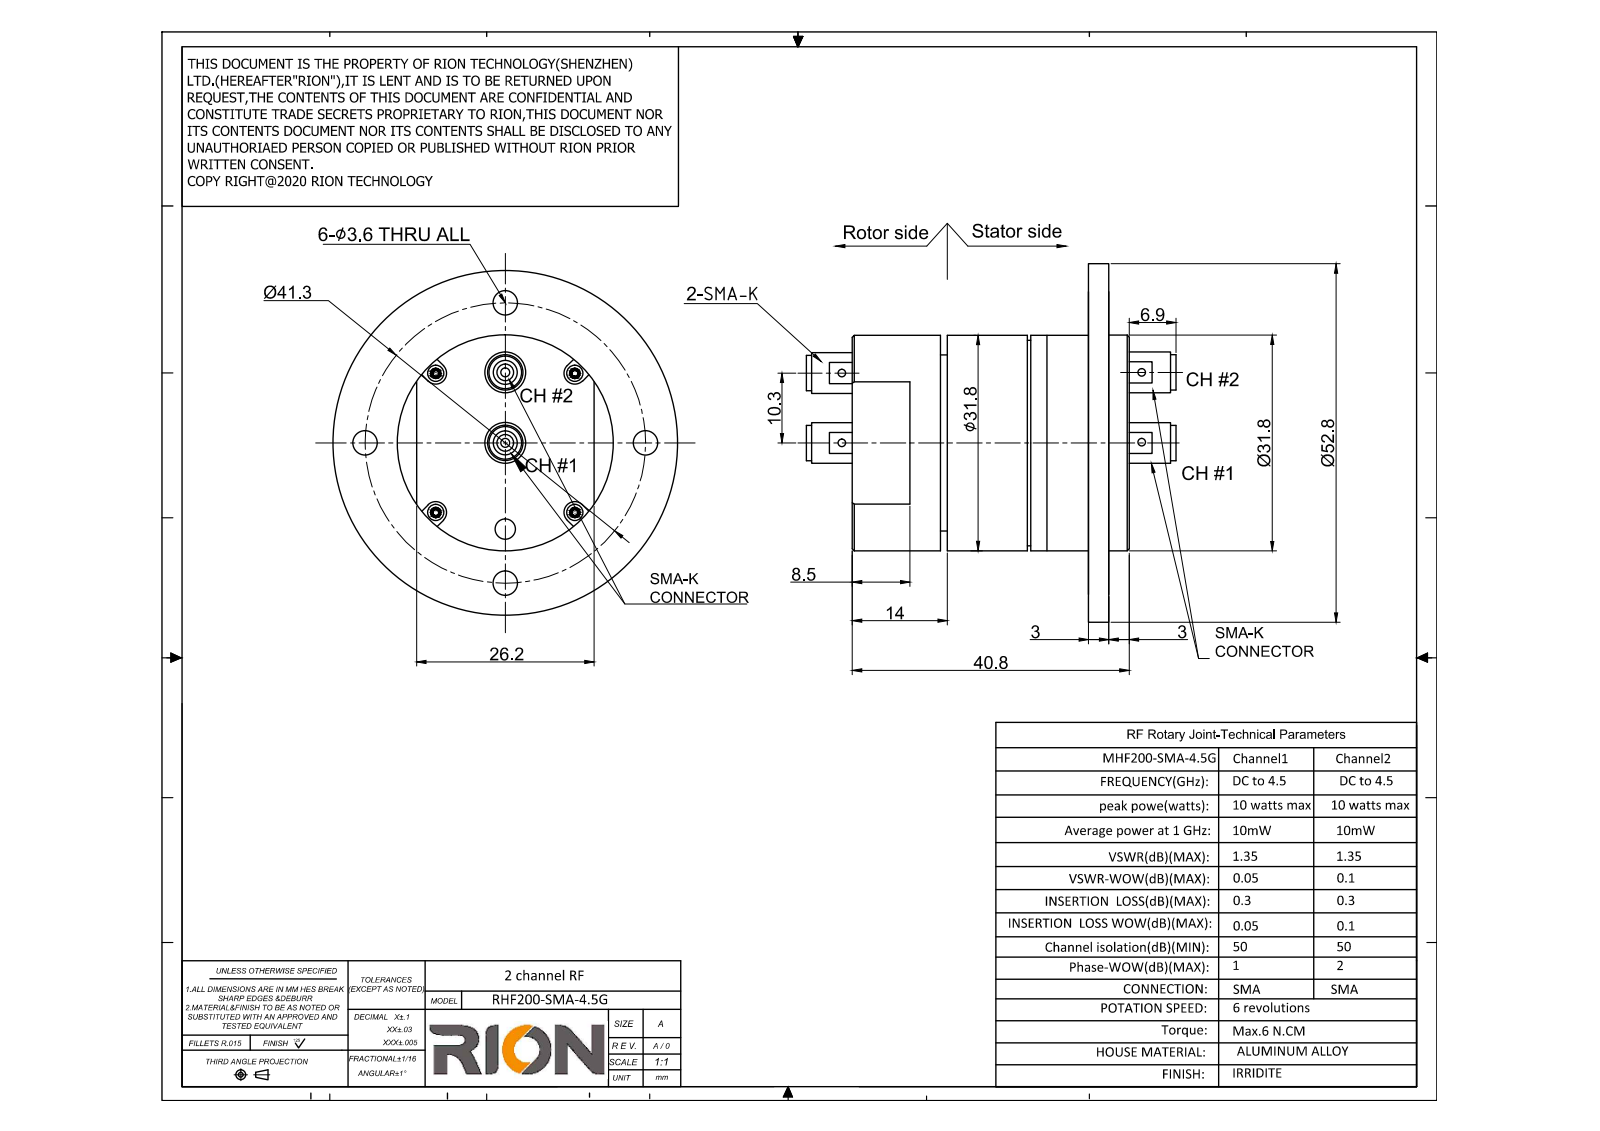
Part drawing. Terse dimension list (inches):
name: RHF200
written by: SolidWorks 2014 (AUTOMOTIVE_DESIGN)
unit: in
bodies: 1 solid, 58 faces (20 planar, 38 cylindrical, 0 other)
size: 2.15 × 2.079 × 2.079
volume: 2.217 in³; area: 15.32 in²
holes: 4× ⌀0.142
bosses: 2× ⌀0.236, 2× ⌀0.205, 1× ⌀2.079, 1× ⌀1.252, 1× ⌀1.181, 1× ⌀1.024
face distances: 0.118, 0.236, 1.37, 1.488, 1.606, 0.512, 0.551, 0.039, 0.858, 0.976
hole spacings: 1.15, 1.626
